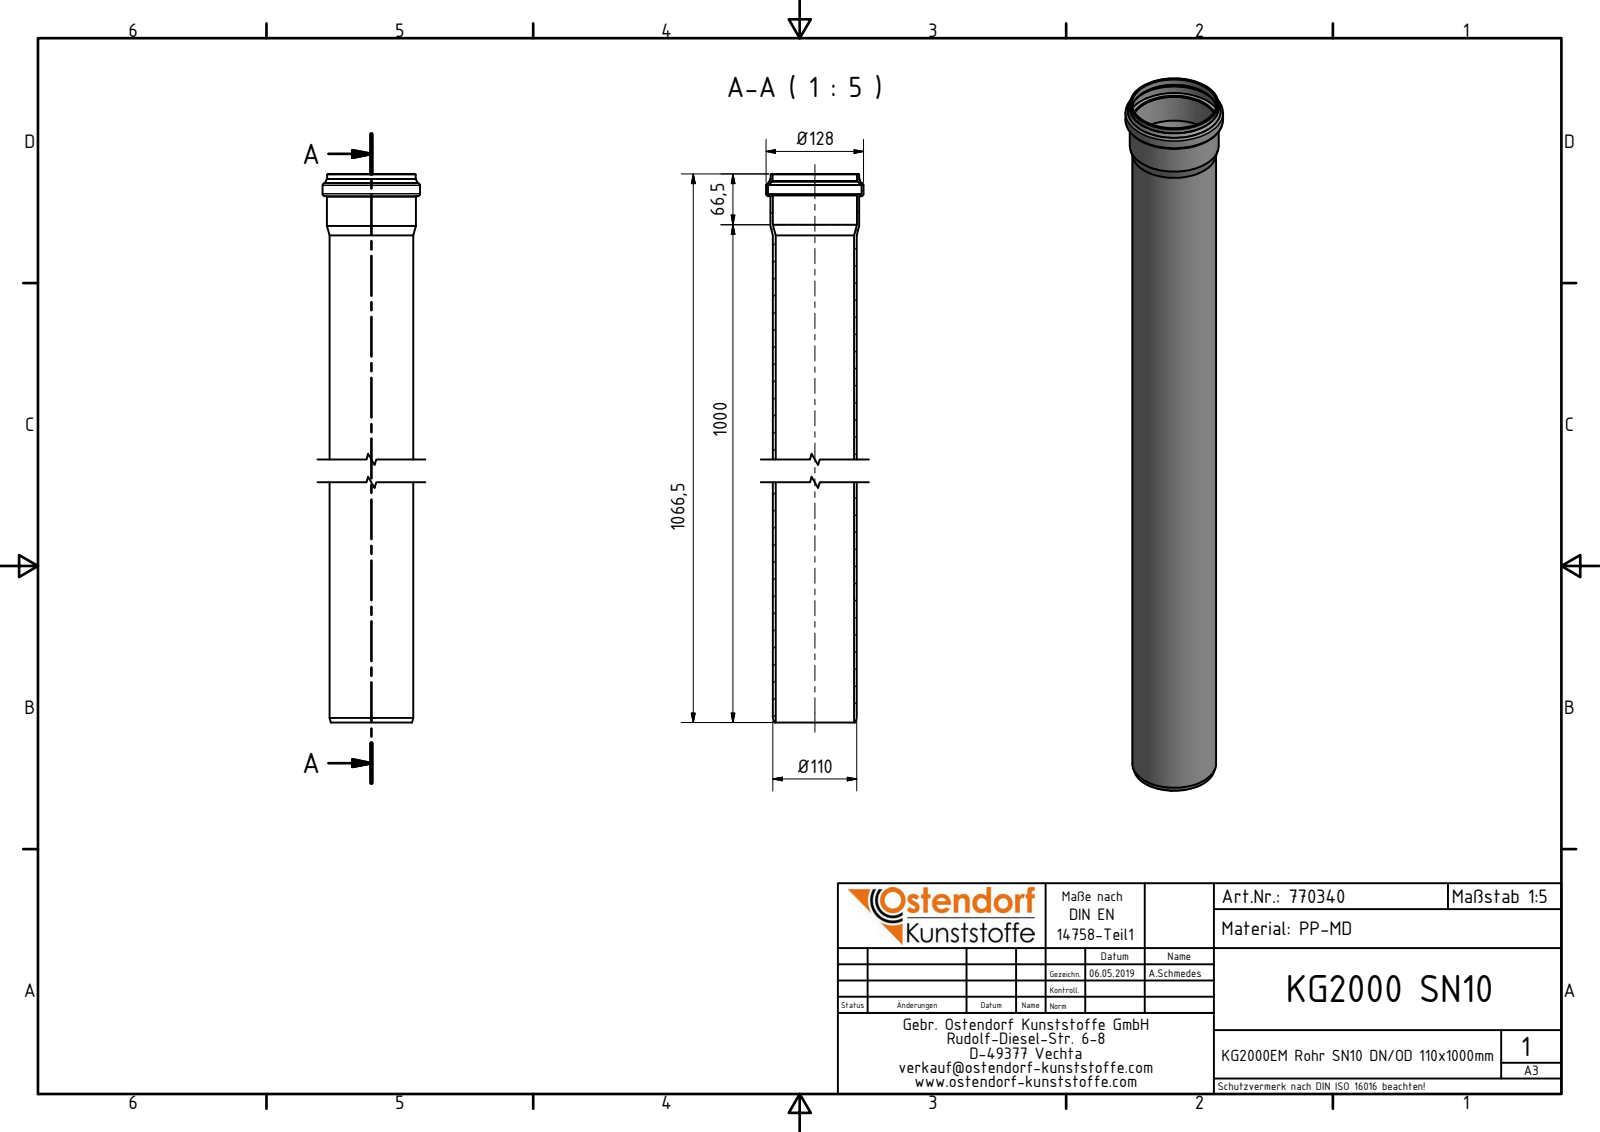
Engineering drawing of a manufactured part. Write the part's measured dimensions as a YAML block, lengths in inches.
part_name: "770340 KG2000EM Rohr SN10 DN-OD110x1000"
step_written_by: "Autodesk Inventor 2016 (AUTOMOTIVE_DESIGN)"
units: inches
bodies: {solids: 1, faces: 37, planar: 6, cylindrical: 9, other: 22}
overall_size: [41.988, 5.039, 5.039]
volume: 76.52
surface_area: 1124
round_holes:
  - {diameter: 4.054, count: 1}
  - {diameter: 4.35, count: 1}
  - {diameter: 4.366, count: 1}
  - {diameter: 4.835, count: 1}
round_bosses_or_shafts:
  - {diameter: 5.039, count: 1}
  - {diameter: 4.594, count: 1}
  - {diameter: 4.571, count: 1}
  - {diameter: 4.331, count: 1}
face_to_face_distances: [40.843, 41.988, 1.146, 40.875, 0.032, 1.113, 41.516, 0.673, 0.641, 0.472]
